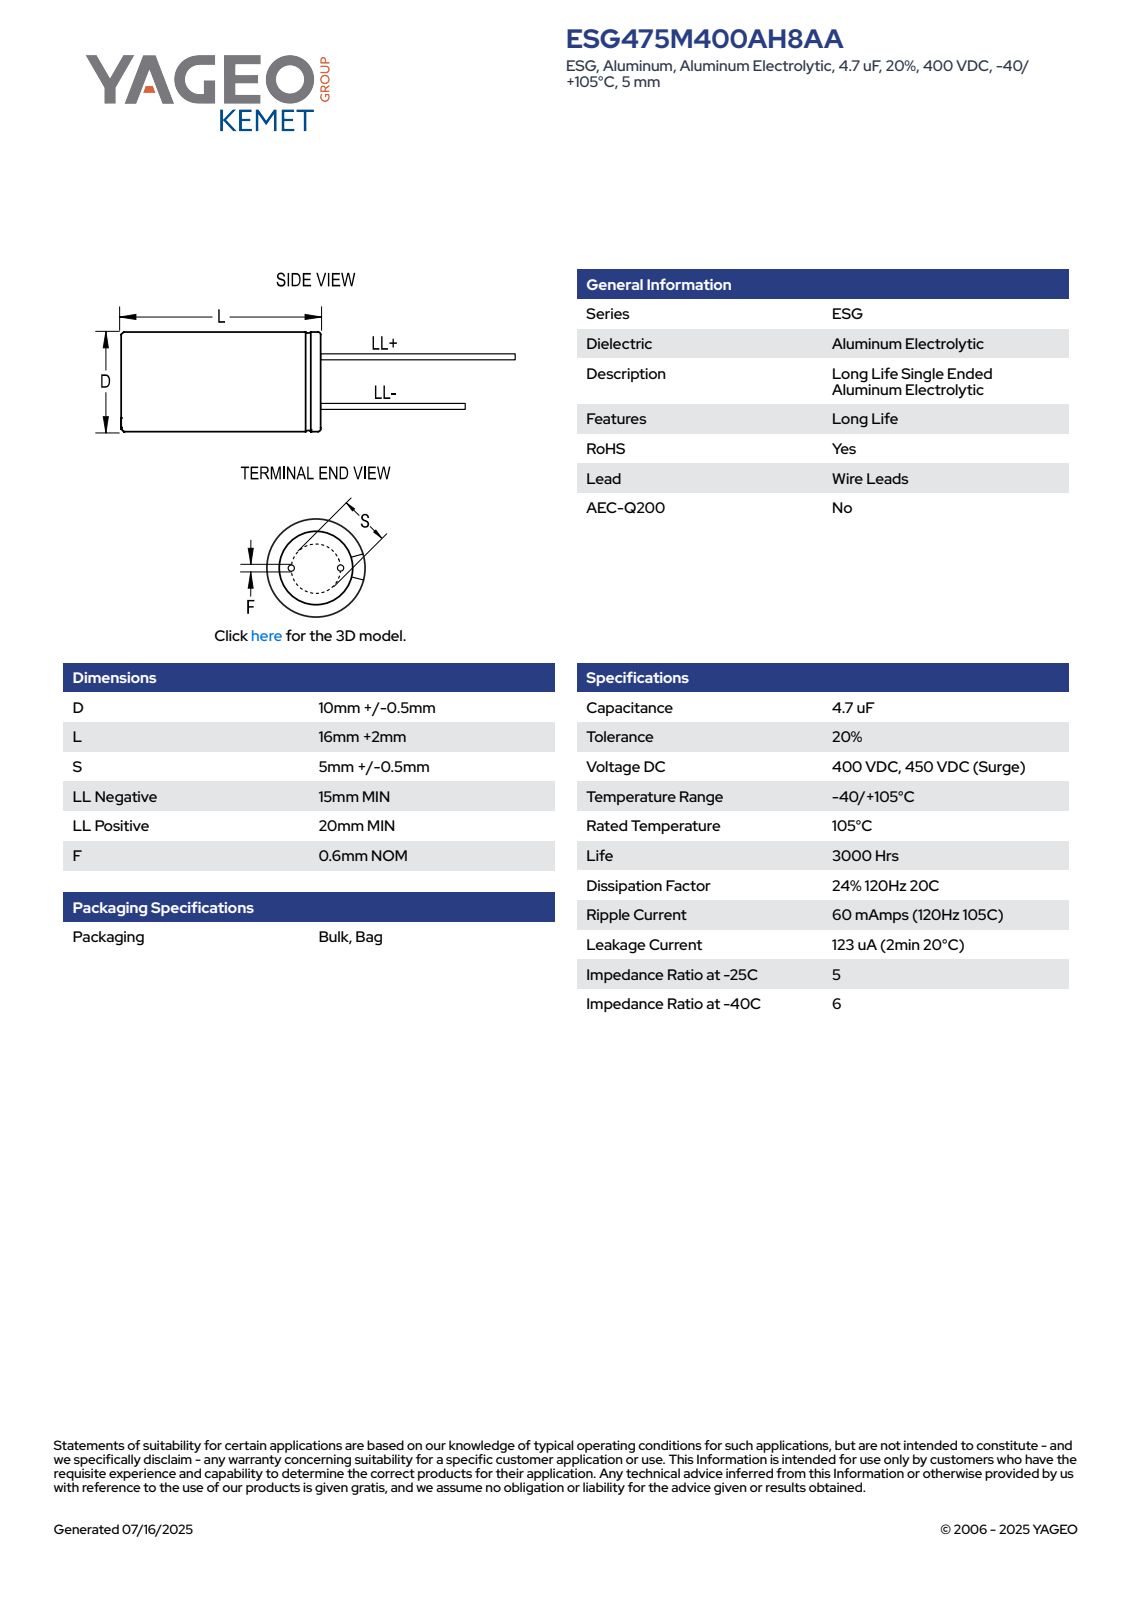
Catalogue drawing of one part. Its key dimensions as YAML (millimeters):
part_name: "CAR_KLP_10X16_D10.5L18S5F0.6"
step_written_by: "SolidWorks 2014 (AUTOMOTIVE_DESIGN)"
units: millimeters
bodies: {solids: 4, faces: 75, planar: 61, cylindrical: 8, other: 6}
overall_size: [38.01, 10.5, 10.5]
volume: 1556
surface_area: 858
round_bosses_or_shafts:
  - {diameter: 0.6, count: 2}
  - {diameter: 10.5, count: 1}
face_to_face_distances: [18, 18.01, 33.01, 38.01, 33, 38, 15, 20, 5, 1.41]
